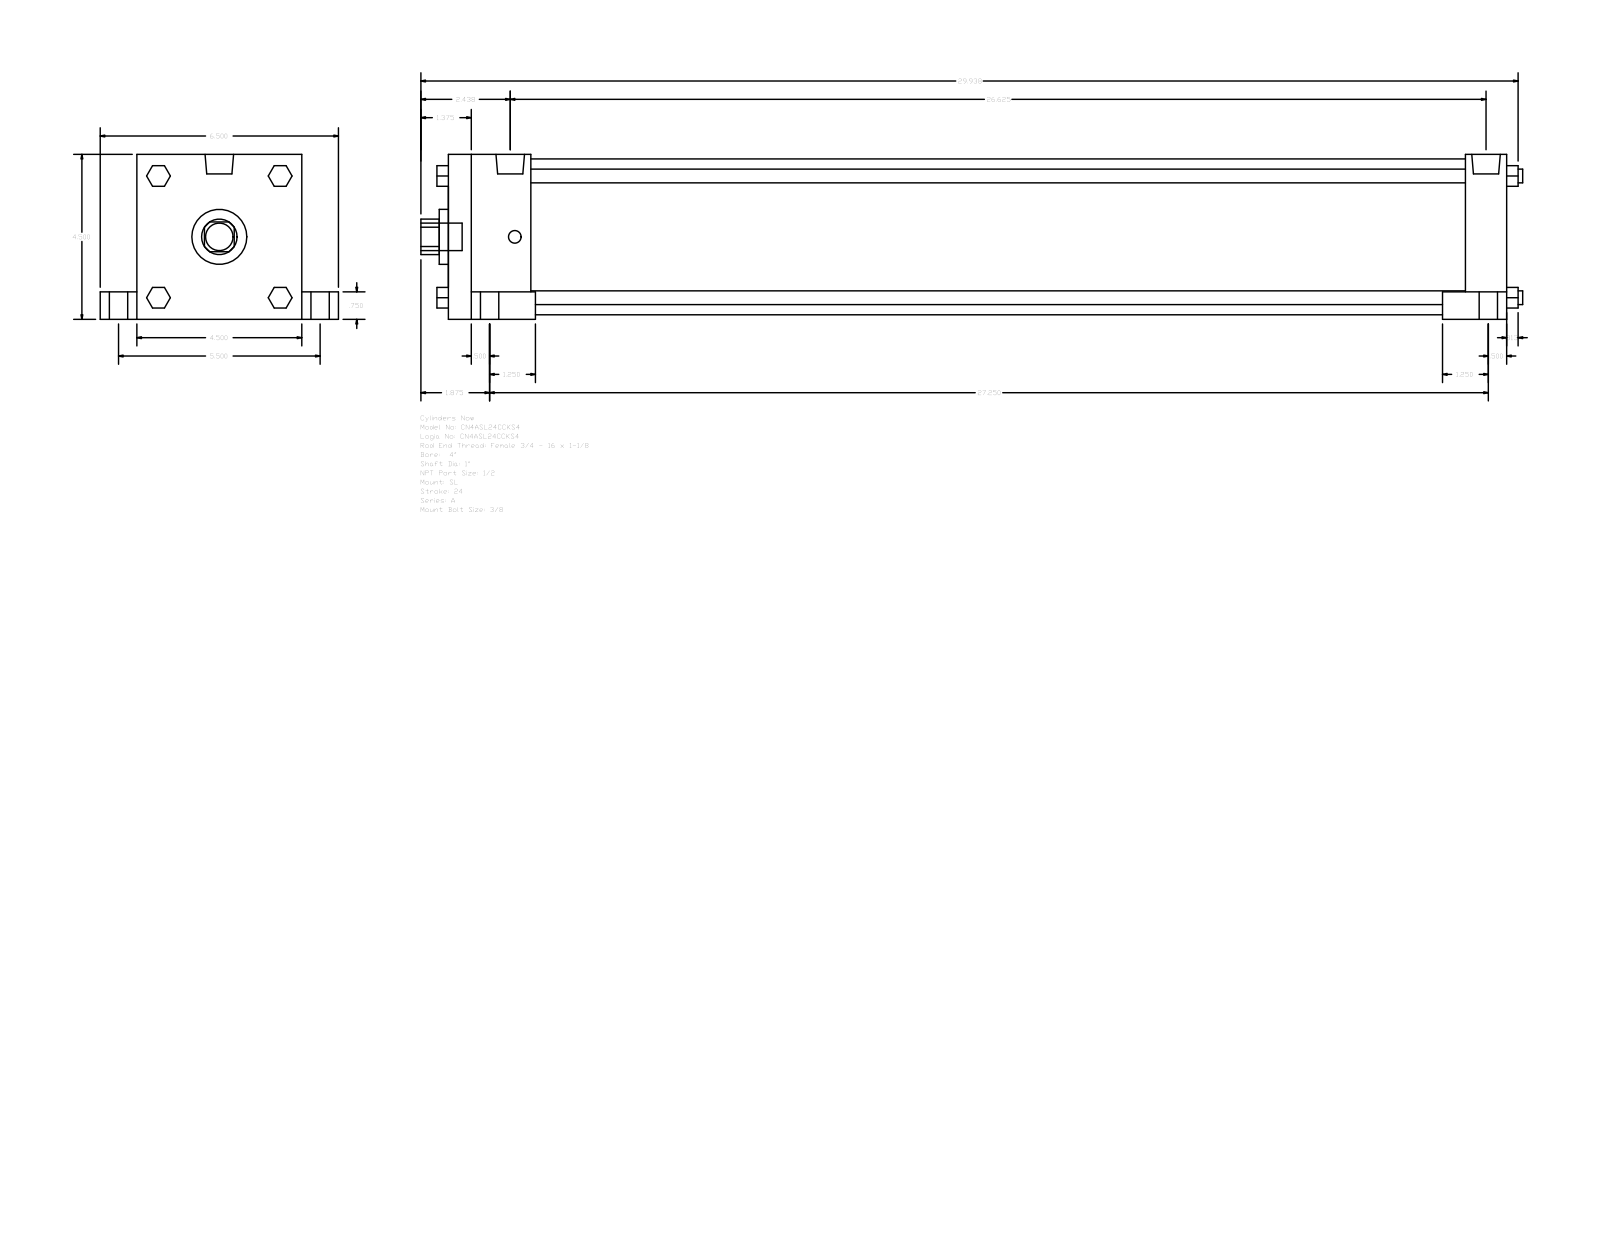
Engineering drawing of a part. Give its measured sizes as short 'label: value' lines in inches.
name: A_SL__0400_1
written by: GSSL Pune (CONFIG_CONTROL_DESIGN)
unit: in
bodies: 0 solids, 150 faces (114 planar, 36 cylindrical, 0 other)
size: 30.063 × 6.5 × 4.5
holes: 1× ⌀1, 1× ⌀1.5, 1× ⌀4.25
bosses: 5× ⌀0.75, 4× ⌀0.5, 4× ⌀0.375, 4× ⌀0.344, 2× ⌀0.778
rounds: 1× R0.484
face distances: 4.5, 28.875, 2.25, 26.625, 27.75, 25.5, 1.125, 0.75, 1, 5.5
